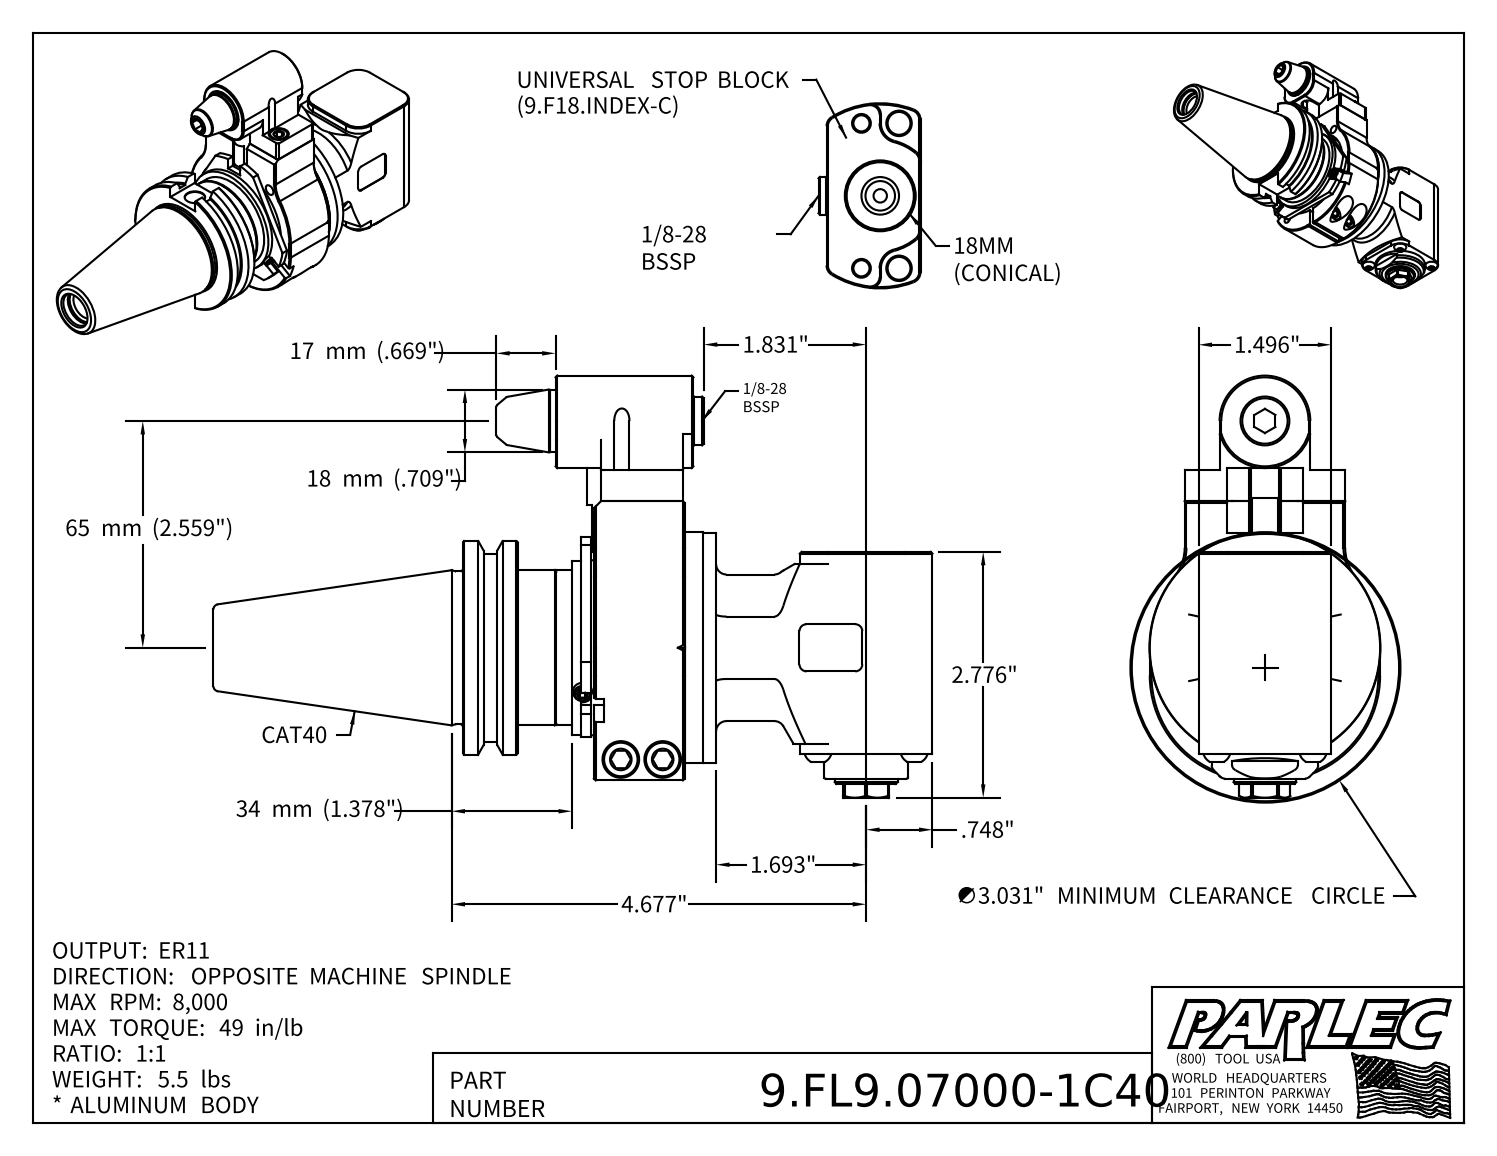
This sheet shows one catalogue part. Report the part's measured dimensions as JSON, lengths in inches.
{"part_name": "9.FL9.07000-1C40; 9_FL9_07000; 9GA05C_446 (Type 0, Cat40, 65mm)", "step_written_by": "Autodesk Inventor 2022 (AUTOMOTIVE_DESIGN)", "units": "inches", "bodies": {"solids": 24, "faces": 727, "planar": 357, "cylindrical": 190, "other": 180}, "overall_size": [8.112, 4.764, 2.606], "volume_in3": 22.61, "surface_area_in2": 169.3, "round_holes": [[0.165, 6], [0.197, 6], [0.126, 4], [0.217, 4], [0.236, 3], [0.13, 2], [0.256, 2], [0.354, 2], [0.37, 2], [0.413, 2], [1.083, 2], [0.098, 1]], "round_bosses_or_shafts": [[0.197, 4], [0.709, 3], [0.394, 3], [0.335, 2], [0.236, 2], [0.157, 2], [2.606, 1], [2.598, 1]], "partial_cylinders_radius": [[0.118, 8], [0.315, 6], [0.039, 4], [0.079, 4], [0.197, 4], [0.512, 3], [0.157, 2], [1.181, 2]], "face_to_face_distances": [0.354, 1.024, 1.378, 1.496, 0.394, 0.571, 0.217, 0.236, 0.945, 1.181], "hole_center_spacings": [0.325, 0.459, 0.473, 0.65, 1.398, 2.58, 2.992, 4.24]}
